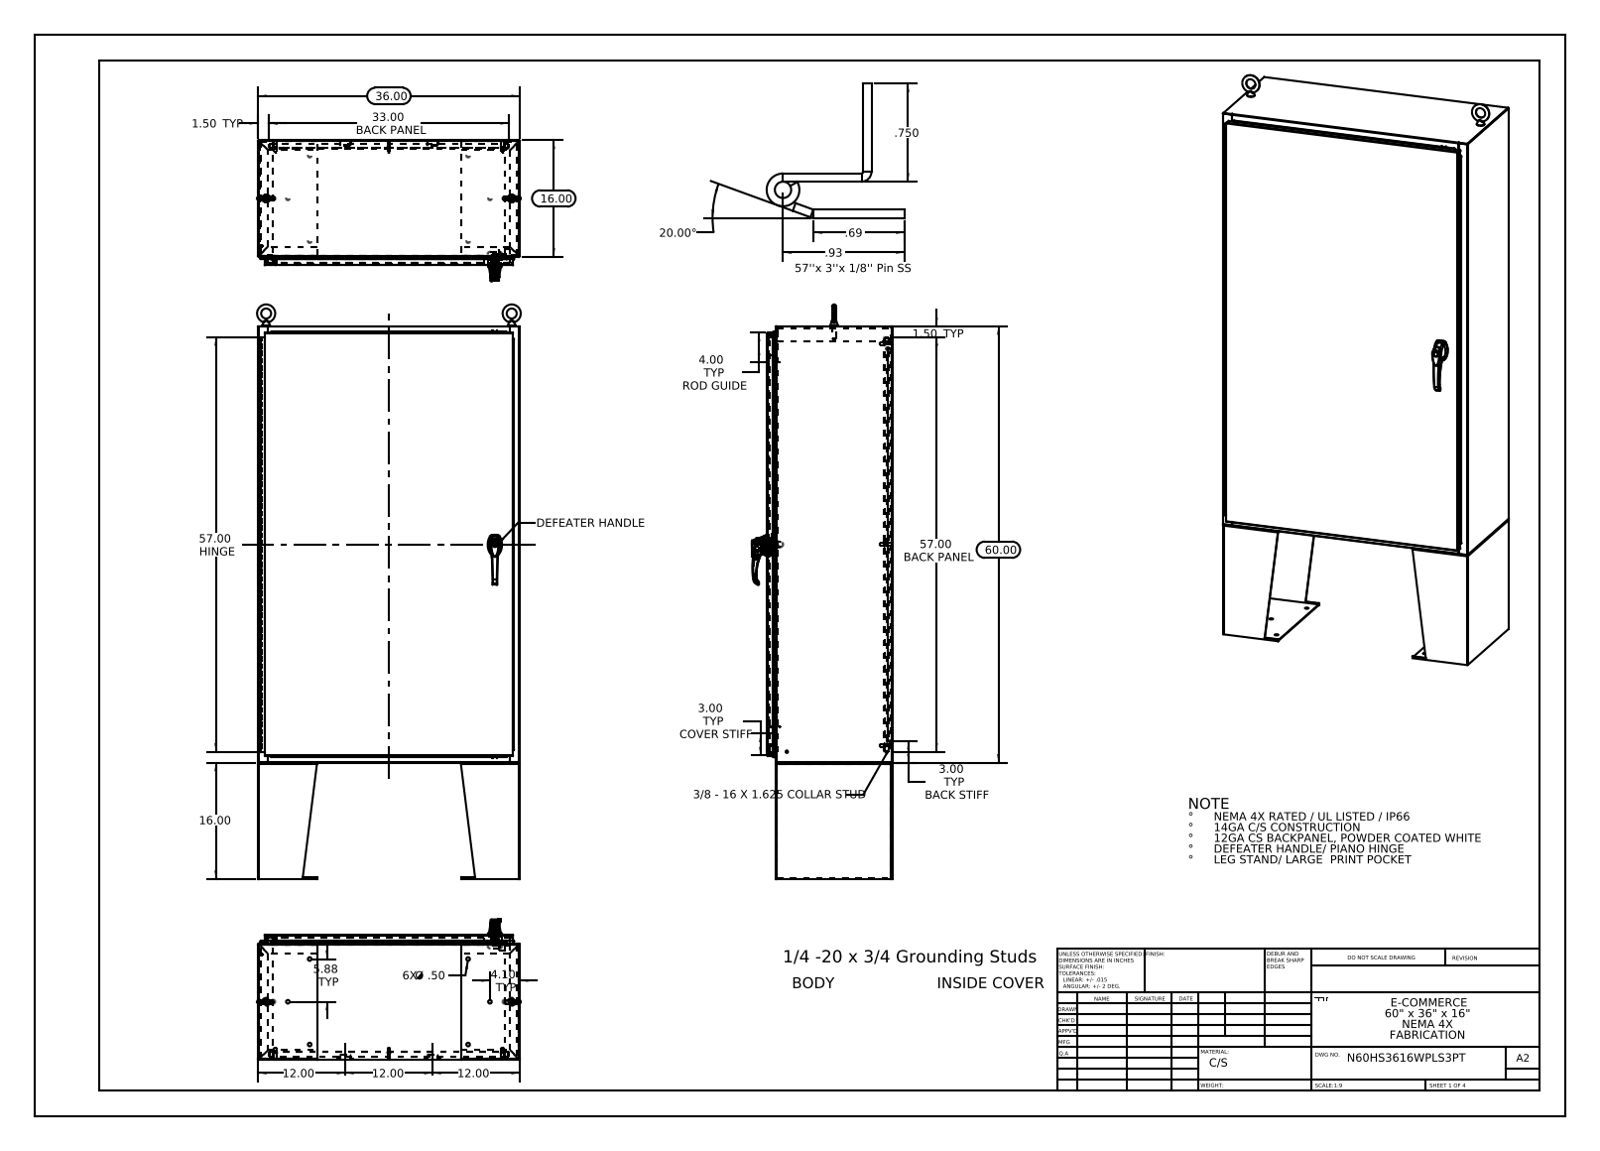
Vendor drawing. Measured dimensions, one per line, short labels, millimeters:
name: HW-EYE-NH-20425_3014T52; N60HS3616SSWPLS3PT Top; N60HS3616SSWPLS3PT Defeater Handle Rod; N60HS3616SSWPLS3PT Mounting Studs (+8 more)
written by: SolidWorks 2013 (CONFIG_CONTROL_DESIGN)
unit: mm
bodies: 55 solids, 3828 faces (1543 planar, 1467 cylindrical, 818 other)
size: 2006.6 × 921.3 × 490.4
volume: 16 500 000 mm³; area: 15 620 000 mm²
holes: 14× ⌀12.7, 10× ⌀6.4, 4× ⌀19.1, 3× ⌀3.5, 3× ⌀4.1, 2× ⌀2, 2× ⌀5.2, 2× ⌀8, 2× ⌀11.1, 1× ⌀3.2, 1× ⌀3.2, 1× ⌀5
bosses: 10× ⌀15.9, 10× ⌀4, 10× ⌀3.6, 8× ⌀9.5, 8× ⌀8.4, 3× ⌀8, 3× ⌀6, 1× ⌀30
rounds: 37× R0.3, 37× R3, 33× R0.2, 31× R2.2, 15× R1, 12× R0.7, 8× R1, 8× R3.6
face distances: 1.9, 435, 2.6, 433.1, 27.3, 436.9, 912.5, 25.4, 407.7, 409.6
hole spacings: 213.2, 344.9, 593.2, 647.2, 651.8, 701.7, 721.3, 1059.4
